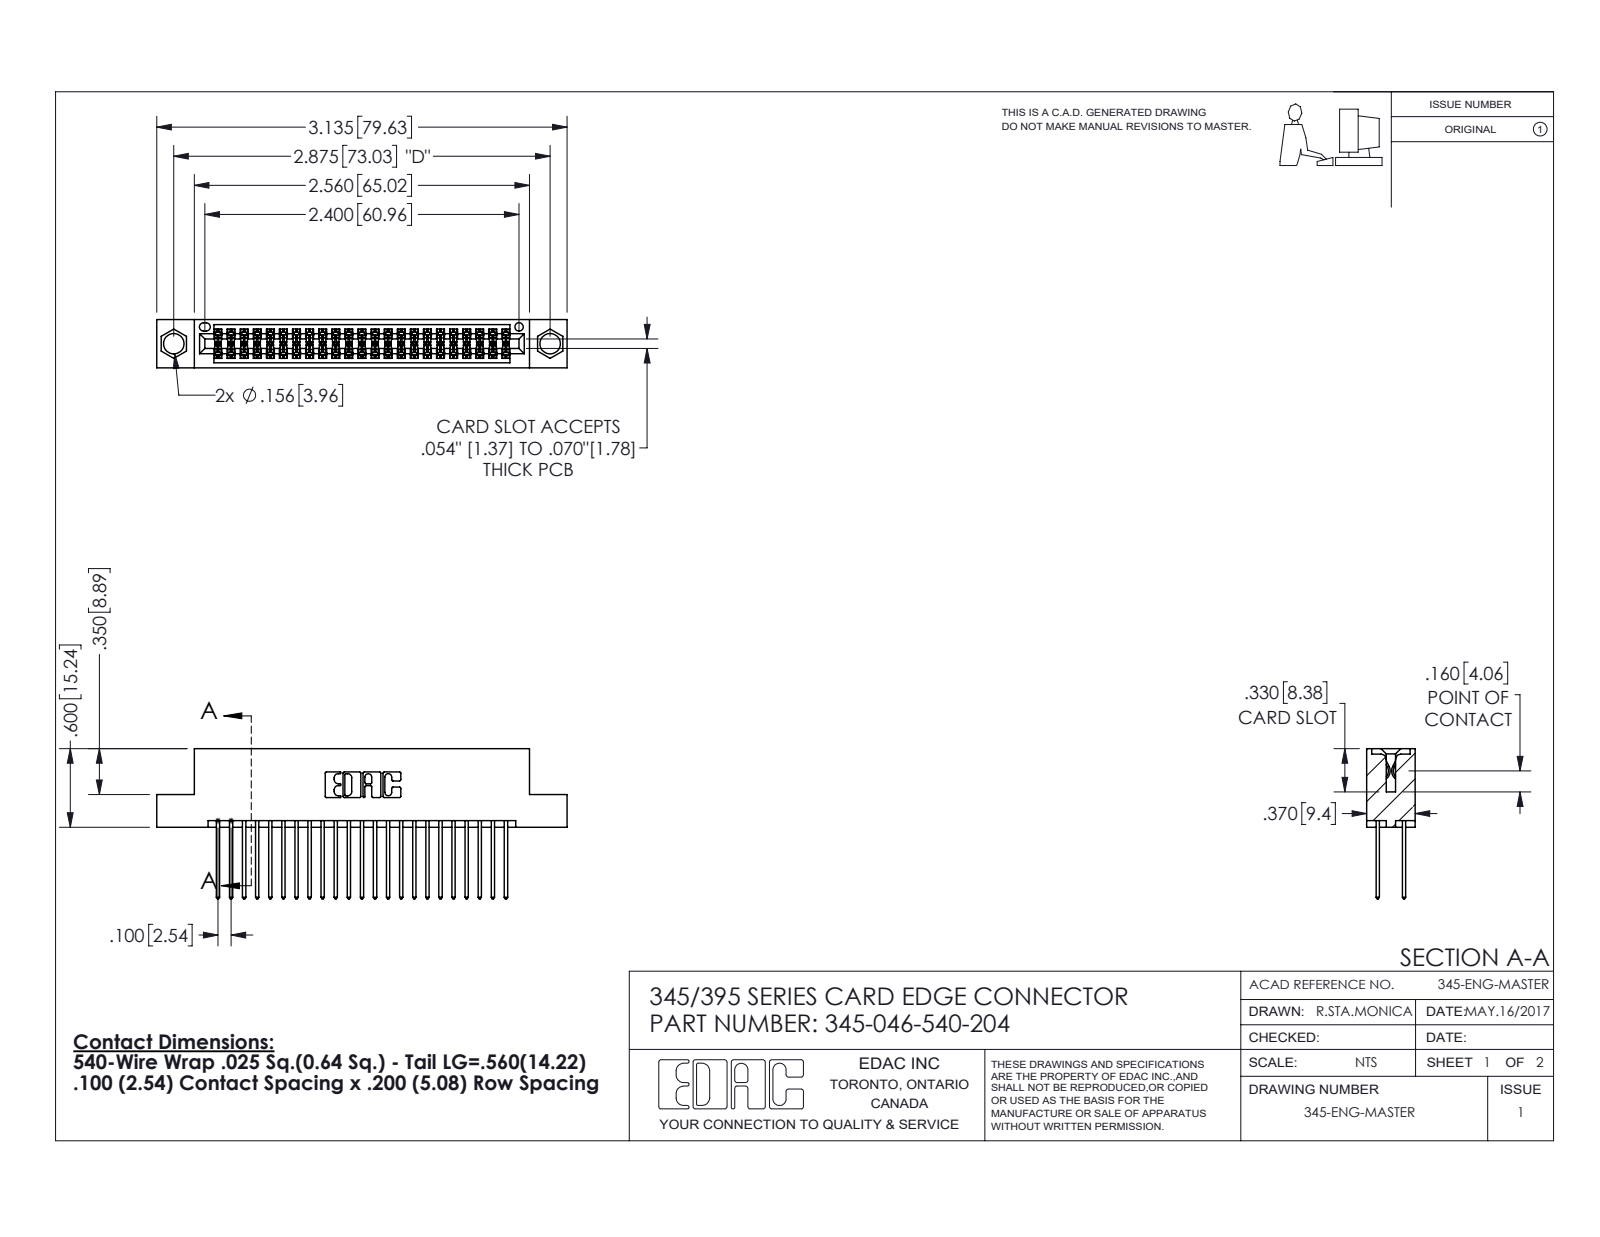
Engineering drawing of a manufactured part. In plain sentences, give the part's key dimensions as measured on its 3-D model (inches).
The part is named "345 Part_Flush Mounting Lugs - 0.156 Dia-TI; 345-292-001_345-293-140; 345-046-540-204". Its 3-D file was written by "SolidWorks 2020 (CONFIG_CONTROL_DESIGN)". It is 47 solids with 2440 faces: 1612 planar, 828 cylindrical and 0 other. Overall it measures 3.135 by 1.147 by 0.37 inches. Its volume is 0.465 cubic inches and its surface area 17.93 square inches. Round holes: 2 of diameter 0.156, 1 of diameter 0.064. Partial cylindrical surfaces (rounded edges, fillets, slot ends): 69 of radius 0.006, 46 of radius 0.01, 22 of radius 0.01, 6 of radius 0.007, 6 of radius 0.031, 3 of radius 0.026, 2 of radius 0.014, 2 of radius 0.019. The main face-to-face distances are 0.298, 0.072, 0.2, 0.098, 0.272, 0.025, 0.37, 0.225, 0.175, 0.149. The hole center spacings are 0.27, 2.641, 2.875.
